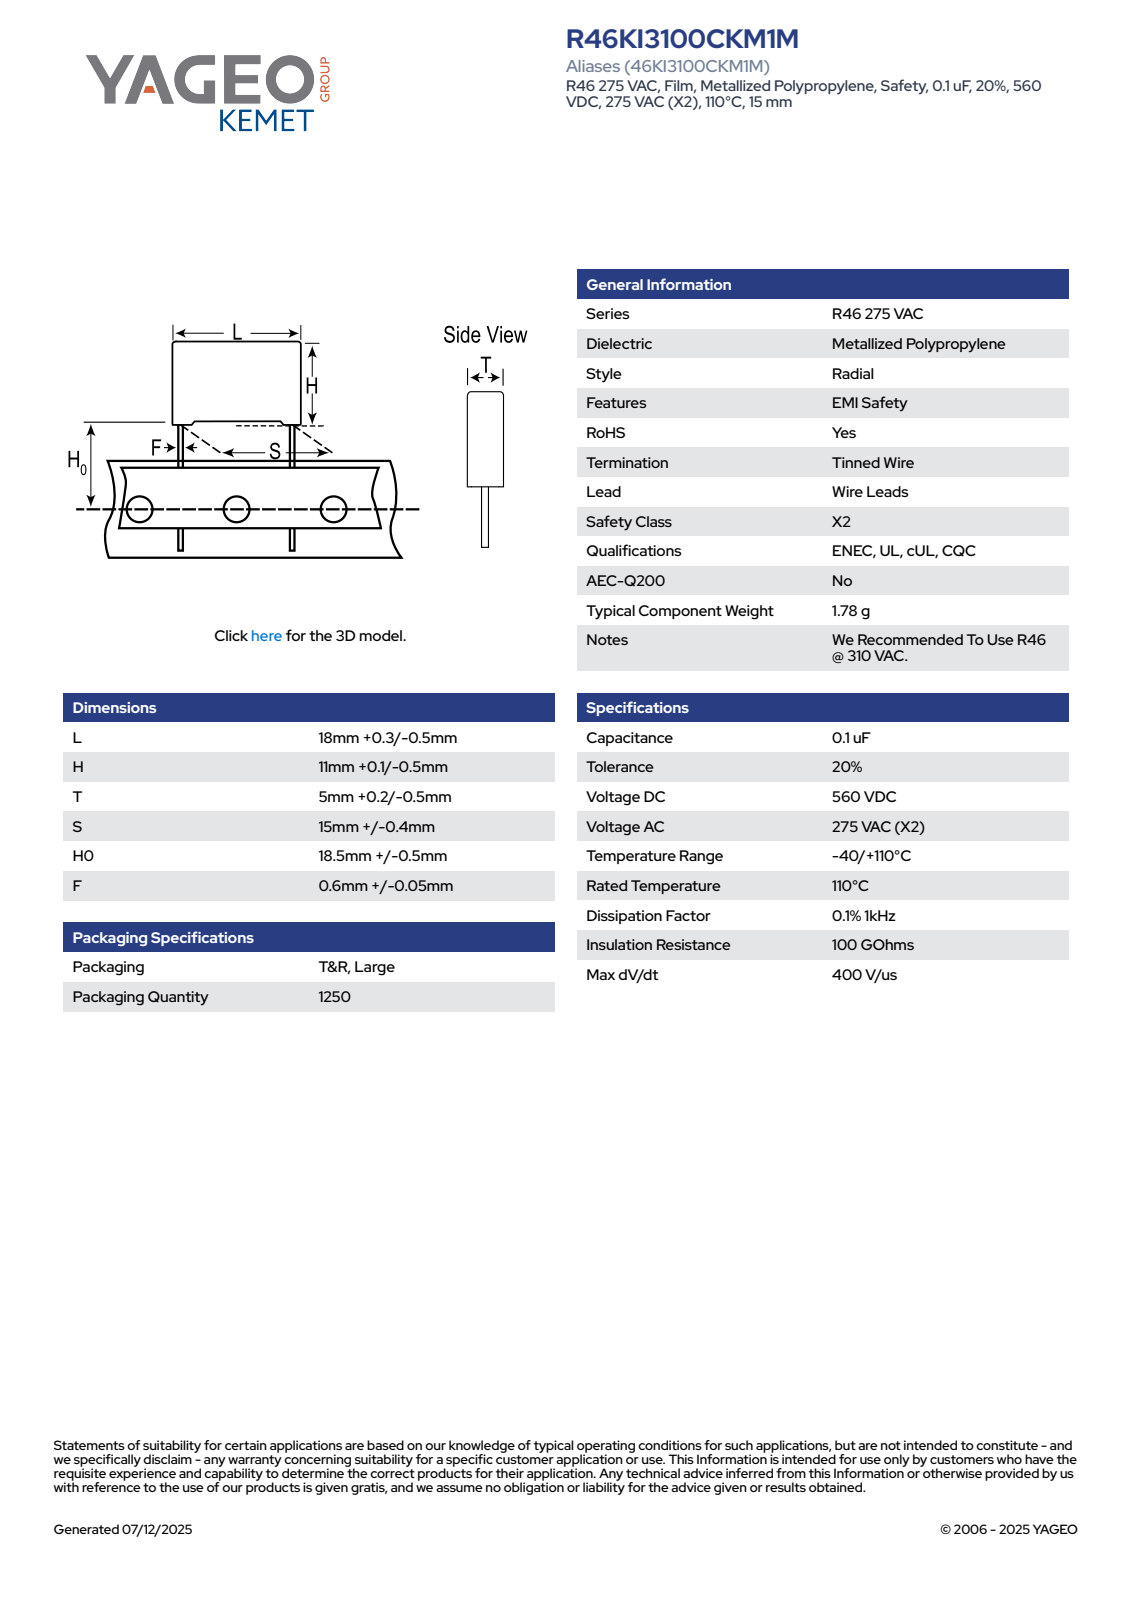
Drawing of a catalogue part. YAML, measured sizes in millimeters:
part_name: "CFR_RB2_18X11X5_L18.3H11.1T5.2S15H019F0.65"
step_written_by: "SolidWorks 2020 (AUTOMOTIVE_DESIGN)"
units: millimeters
bodies: {solids: 4, faces: 85, planar: 77, cylindrical: 8, other: 0}
overall_size: [30.1, 18.3, 5.21]
volume: 1011
surface_area: 822
round_bosses_or_shafts:
  - {diameter: 0.65, count: 2}
partial_cylinders:
  - {radius: 0.5, count: 4}
face_to_face_distances: [5.2, 10.35, 18.3, 0.61, 4.59, 0.37, 10.72, 0.38, 0.75, 11.1]
